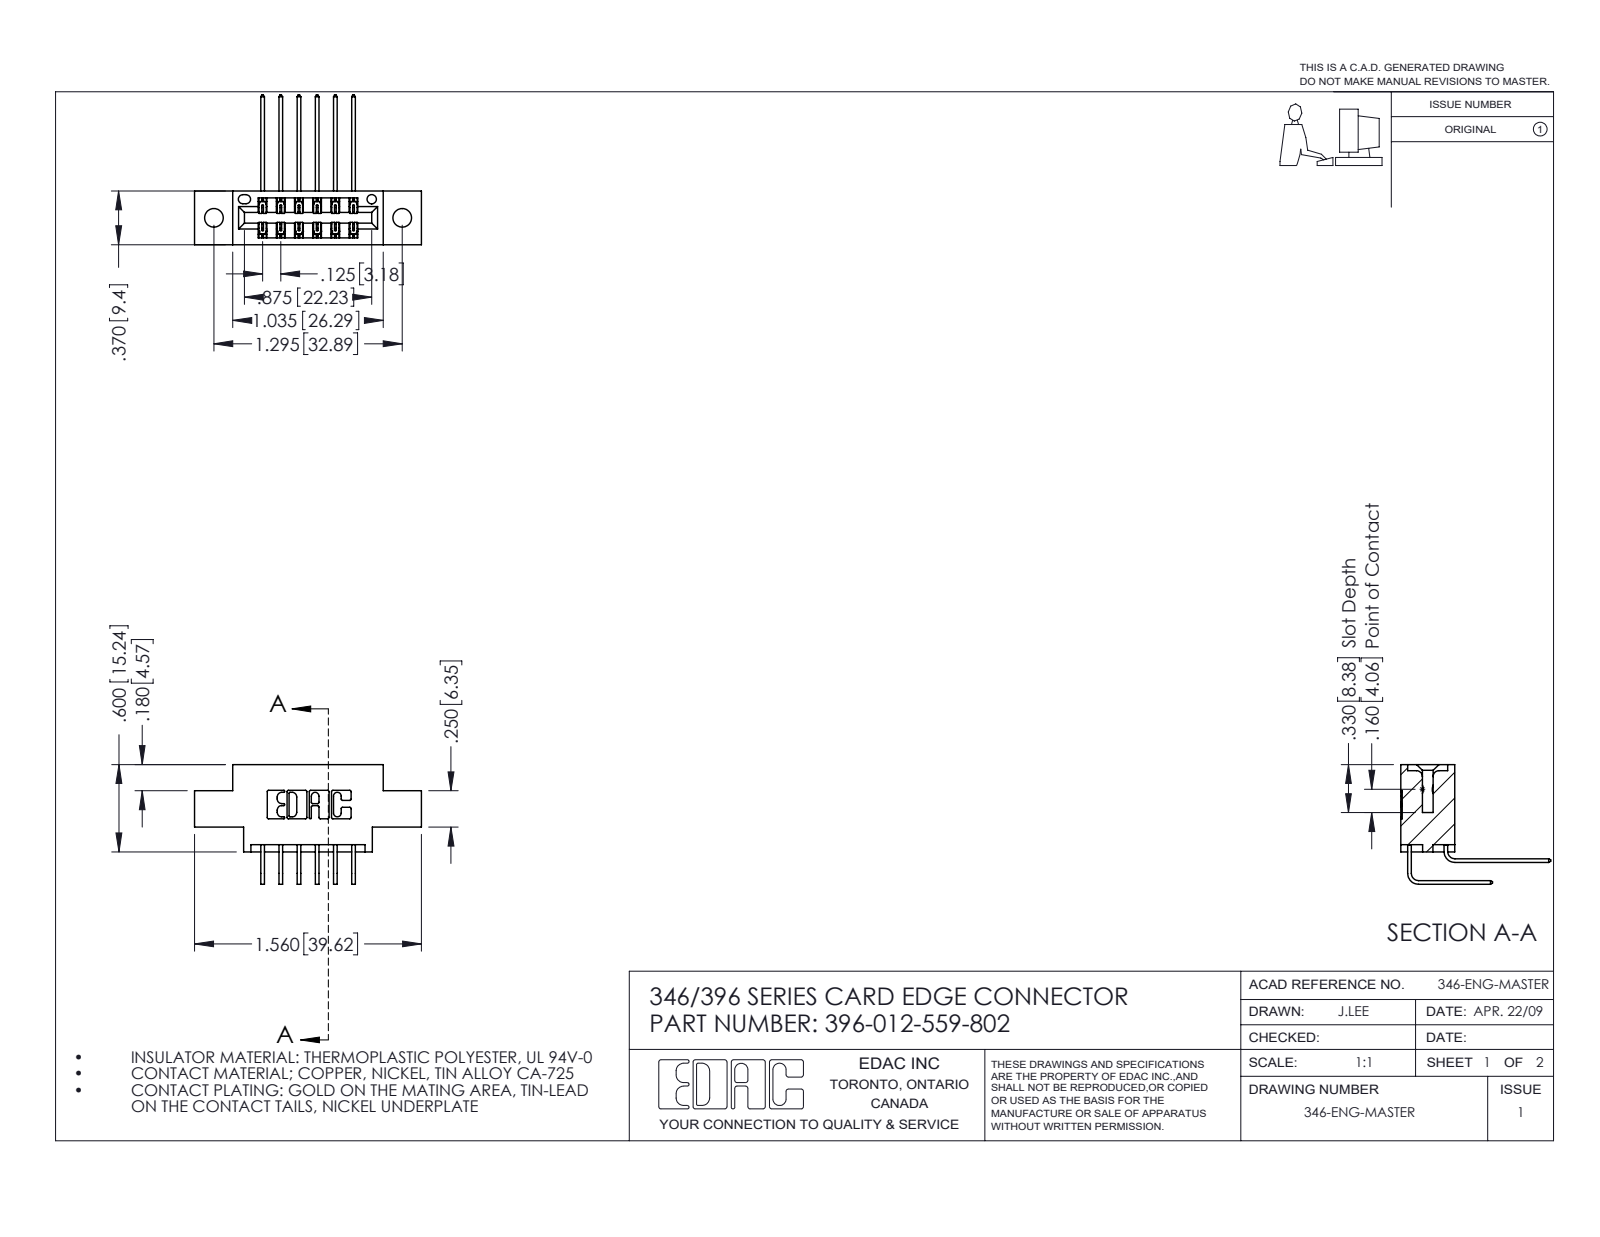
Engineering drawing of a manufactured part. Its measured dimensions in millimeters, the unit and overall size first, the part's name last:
Units: millimetres
Overall size (bounding box): 39.6 × 26.2 × 20.9
Round holes (diameter × count): ⌀3.3 ×2, ⌀1.6 ×1
Partial cylindrical surfaces — rounded edges, fillets, slot ends (radius × count): R0.3 ×22, R0.2 ×18, R0.2 ×6, R0.8 ×6, R0.7 ×3, R0.4 ×2, R0.6 ×2, R0.6 ×2
Main face-to-face distances: 6.4, 9.4, 1.2, 8.2, 0.6, 1.8, 3.2, 7.6, 3.8, 5.6
Hole centre spacings: 6.2, 27.7, 32.9
Volume: 3 460 mm³ · Surface area: 4 435 mm²
Bodies: 13 solids, 774 faces (524 planar, 250 cylindrical, 0 other)
Part name (STEP PRODUCT): 396-012-559-802; 345-292-001_558 559 Tail - 1; 345-292-001_559 Tail - 2; 346 Part_0.170 Offset - 0.128 Dia
STEP written by: SolidWorks 2016 (CONFIG_CONTROL_DESIGN)
